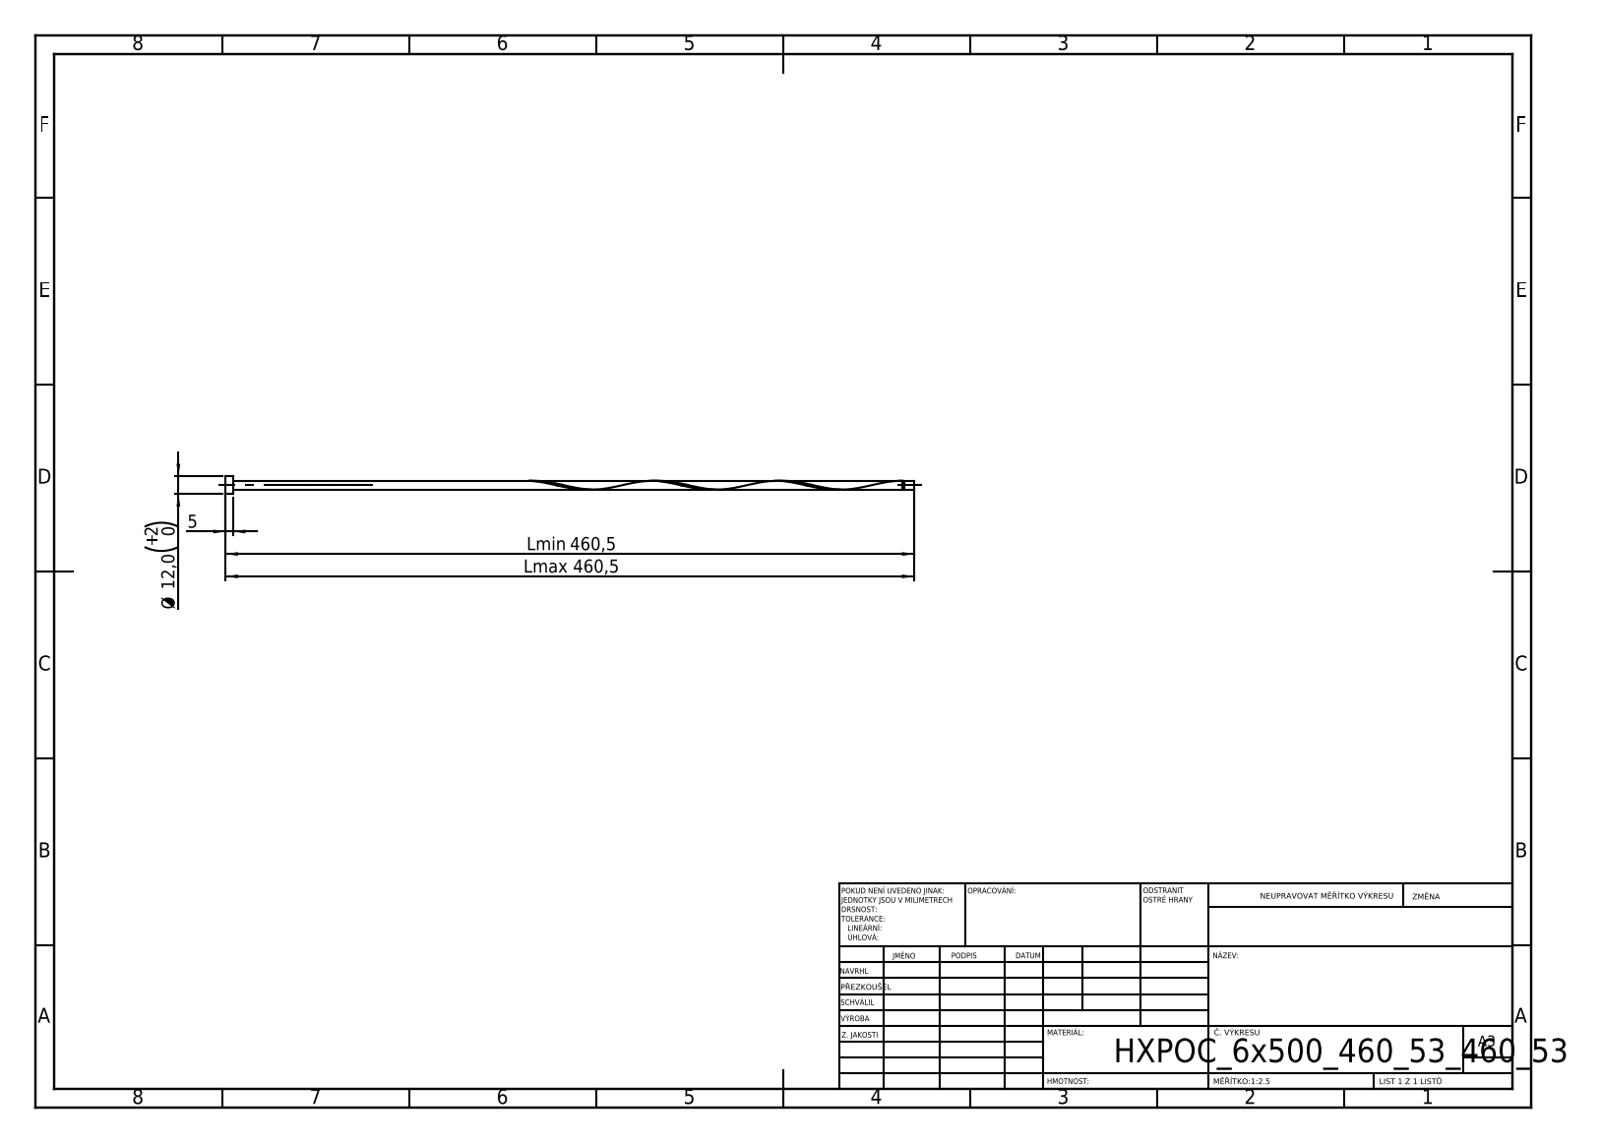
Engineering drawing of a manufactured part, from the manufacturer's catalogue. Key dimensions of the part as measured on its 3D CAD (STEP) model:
STEP written by: SolidWorks 2019 (CONFIG_CONTROL_DESIGN)
Units: millimetres
Bodies: 1 solid, 16 faces (6 planar, 9 cylindrical, 1 other)
Overall size (bounding box): 460.53 × 12 × 12
Volume: 16 439 mm³ · Surface area: 12 304 mm²
Round bosses / shafts (diameter × count): ⌀12 ×1, ⌀6 ×1, ⌀4.8 ×1
Main face-to-face distances: 5, 460.53, 455.53, 453.92, 448.92, 6.61, 452.72, 447.72, 1.2, 7.81
